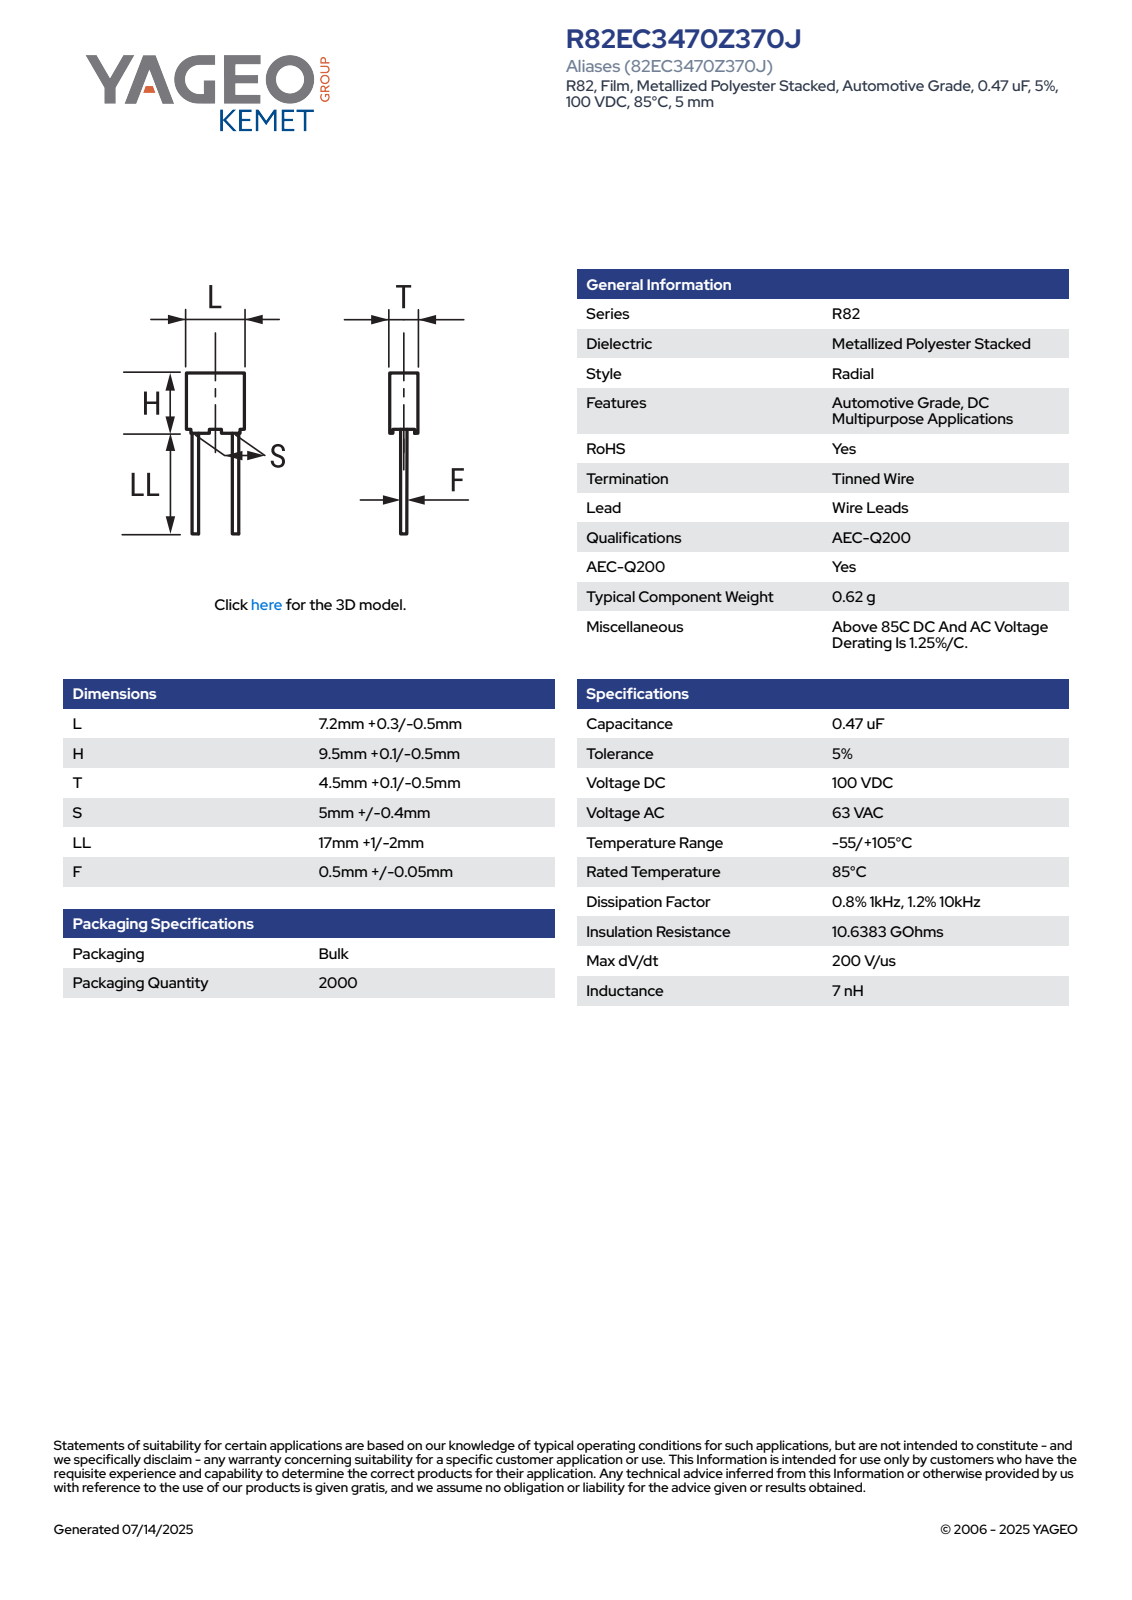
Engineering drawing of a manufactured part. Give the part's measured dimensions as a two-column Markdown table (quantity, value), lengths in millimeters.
| quantity | value |
| --- | --- |
| part name | CFR_RB3_7.2X9.5X4.5_L7.5H9.6T4.6S5LL18F0.55 |
| STEP written by | SolidWorks 2014 (AUTOMOTIVE_DESIGN) |
| units | millimeters |
| bodies | 4 solids, 85 faces (77 planar, 8 cylindrical, 0 other) |
| overall size | 27.6 × 7.5 × 4.61 |
| volume | 317 mm³ |
| surface area | 380 mm² |
| round bosses / shafts (diameter × count) | 0.55 × 2 |
| partial cylindrical surfaces (radius × count) | 0.5 × 4 |
| main face-to-face distances | 4.6, 7.5, 8.85, 4.35, 7.25, 0.75, 9.6, 4.1, 7, 0.33 |
